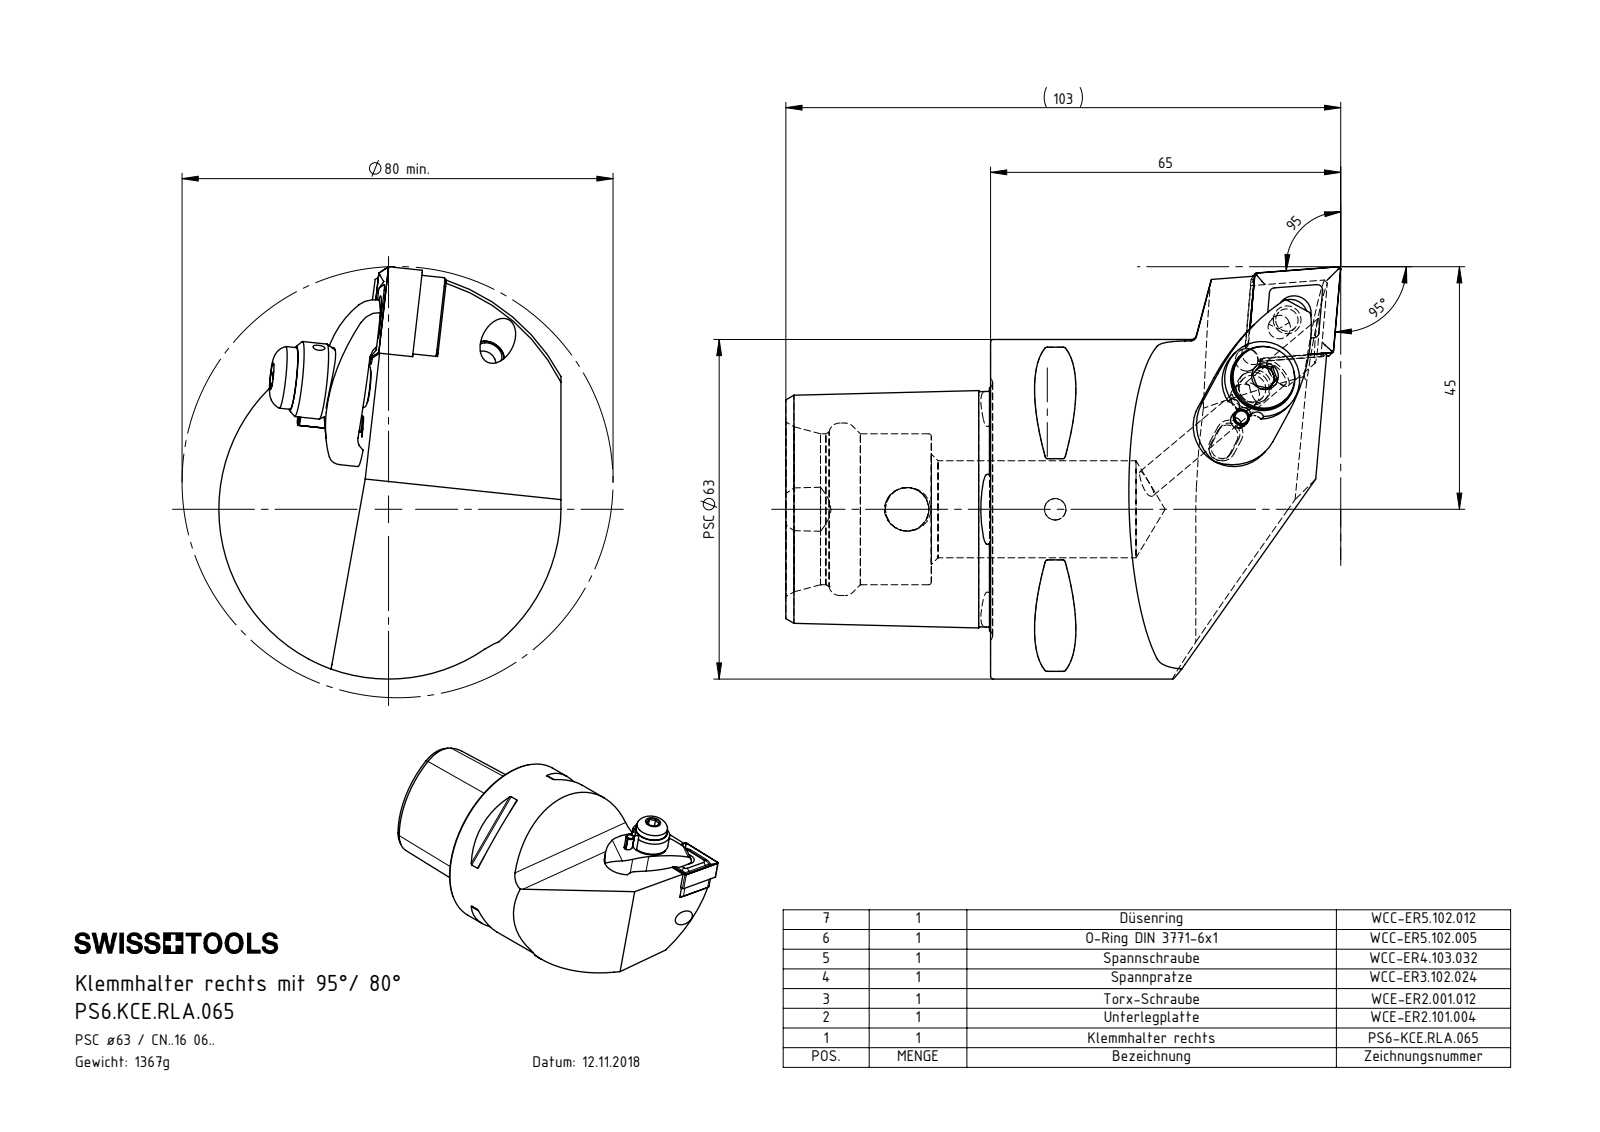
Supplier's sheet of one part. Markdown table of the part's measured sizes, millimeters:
| quantity | value |
| --- | --- |
| part name | WCC-ER4.103.032_A; KVT_MB_600_060; ISO 13337 - 3 x 12_PreviewCfg; CNMG160604 (+7 more) |
| STEP written by | SolidWorks 2017 (AUTOMOTIVE_DESIGN) |
| units | millimeters |
| bodies | 11 solids, 306 faces (97 planar, 86 cylindrical, 123 other) |
| overall size | 103 × 76.5 × 63.5 |
| volume | 174 681 mm³ |
| surface area | 33 838 mm² |
| round holes (diameter × count) | 2 × 3, 5 × 3, 4.2 × 2, 7 × 2, 2.4 × 1, 3 × 1, 4 × 1, 6 × 1, 6.2 × 1, 6.35 × 1, 8.05 × 1, 8.1 × 1 |
| round bosses / shafts (diameter × count) | 6 × 2, 3 × 2, 63 × 1, 14 × 1, 11.5 × 1, 6.8 × 1, 6.2 × 1, 5 × 1 |
| partial cylindrical surfaces (radius × count) | 0.5 × 8, 1.5 × 7, 0.45 × 6, 0.4 × 4, 0.79 × 4, 6 × 3, 0.79 × 2, 2 × 2 |
| main face-to-face distances | 38, 6.06, 24.88, 27, 11, 14.65, 7.35, 1.29, 4.79, 10.85 |
| hole center spacings | 6.15, 7.99, 8, 8.2, 13.64, 15.4, 5.97, 10.59 |
